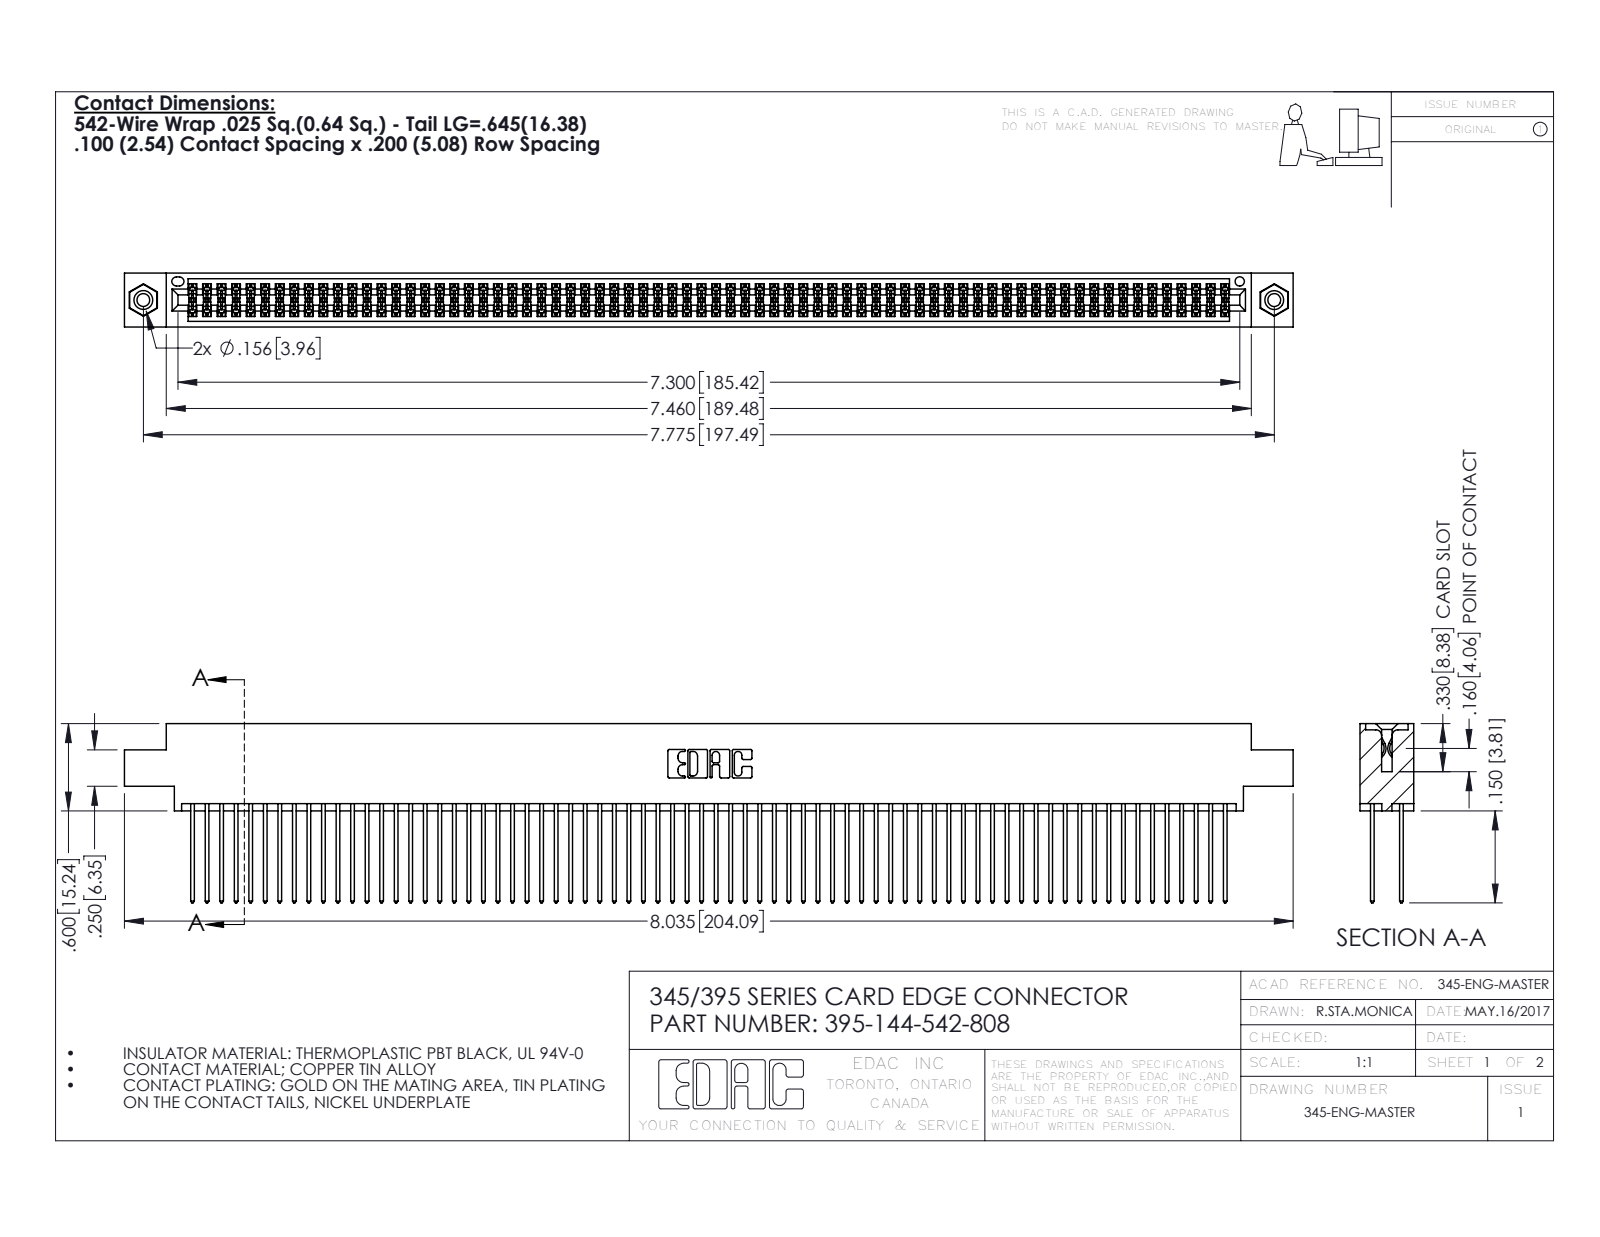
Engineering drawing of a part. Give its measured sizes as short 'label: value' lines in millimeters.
name: 345 Part_0.170 Offset - 0.156 Dia-TI; 345-292-001_345-293-142; 345-250-001_345-250-003-102; 395-144-542-808
written by: SolidWorks 2016 (CONFIG_CONTROL_DESIGN)
unit: mm
bodies: 147 solids, 7390 faces (4868 planar, 2506 cylindrical, 16 other)
size: 204.1 × 31.3 × 9.4
volume: 20 650 mm³; area: 34 410 mm²
holes: 2× ⌀2.3, 2× ⌀3.2, 2× ⌀4, 1× ⌀1.6
bosses: 2× ⌀3.9
rounds: 216× R0.2, 144× R0.3, 22× R0.3, 6× R0.2, 6× R0.8, 3× R0.7, 2× R0.4, 2× R0.5
face distances: 1.8, 7.6, 5.1, 2.5, 6.9, 0.6, 5.7, 9.4, 4.4, 3.8
hole spacings: 6.9, 191.5, 197.5
